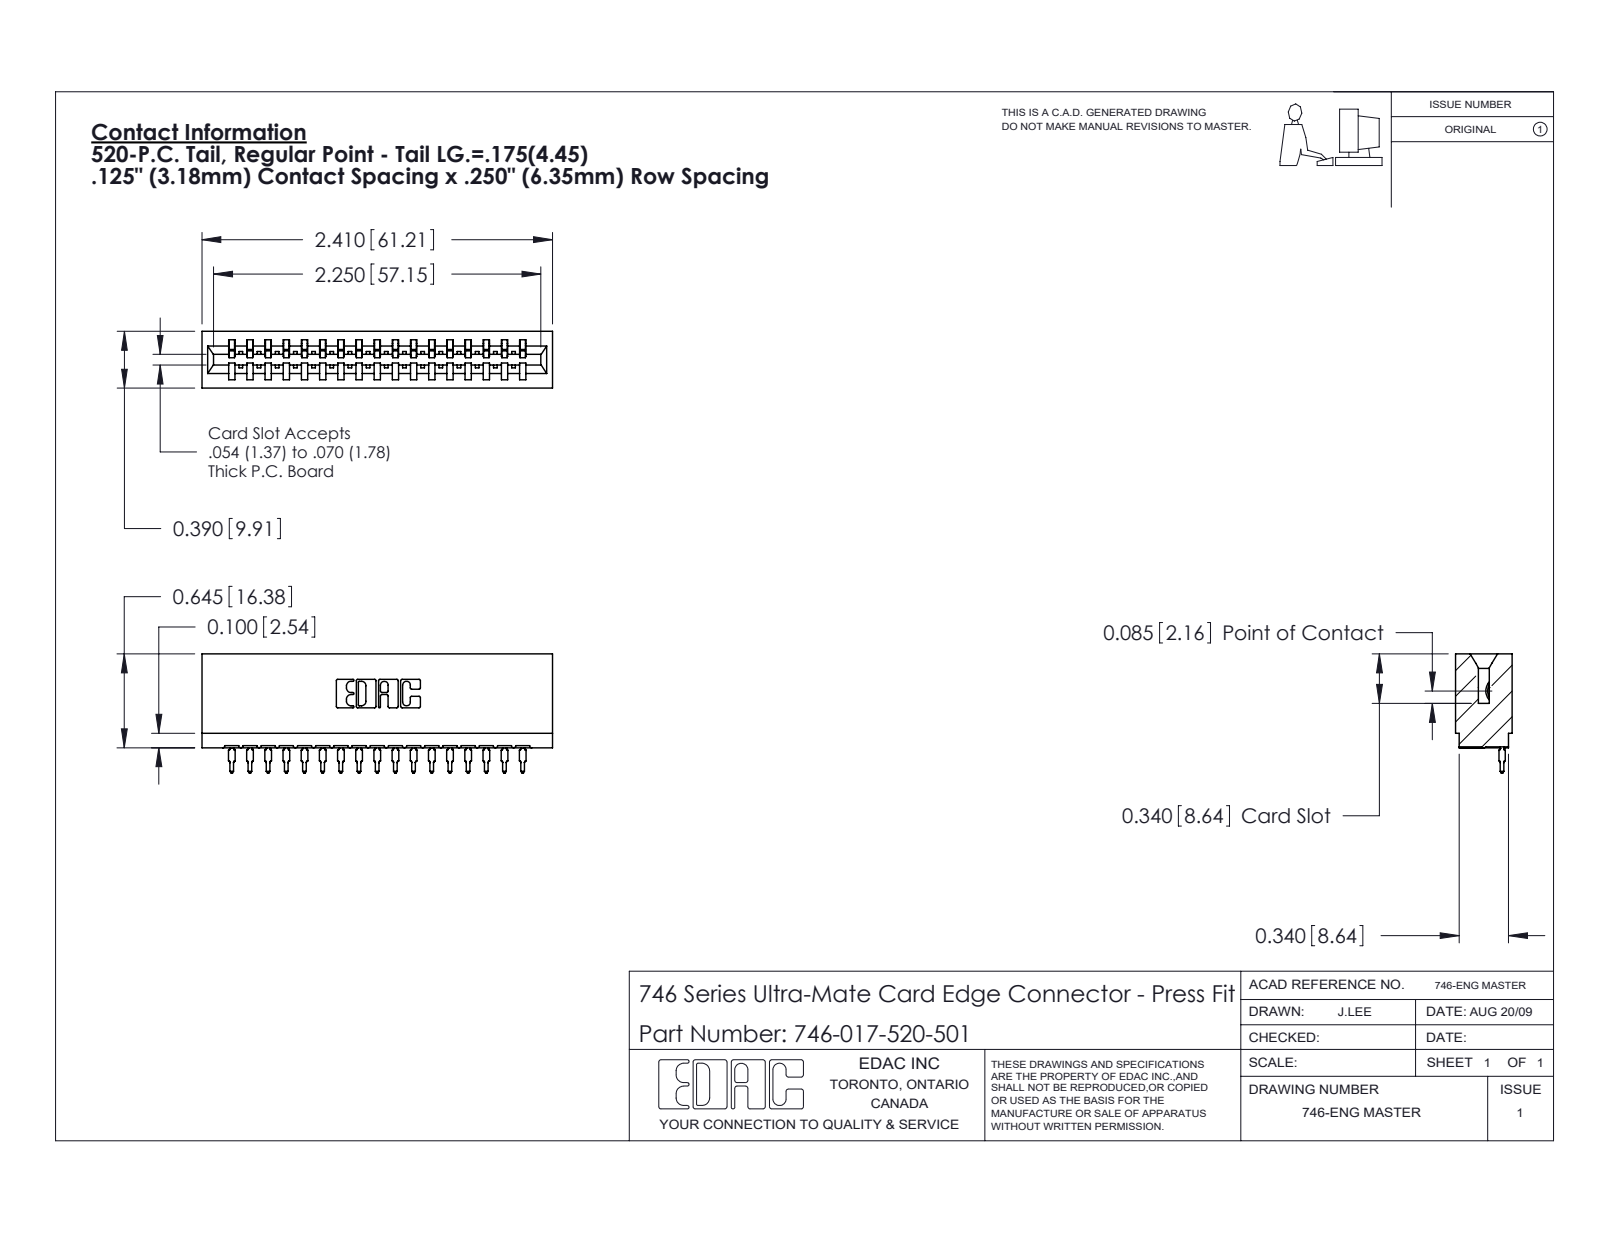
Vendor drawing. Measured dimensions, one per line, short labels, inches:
name: 746-292-001_520; 746-017-520-501; 746 Part_.340 Slot Depth - 01
written by: SolidWorks 2020 (CONFIG_CONTROL_DESIGN)
unit: in
bodies: 18 solids, 1933 faces (1126 planar, 365 cylindrical, 442 other)
size: 2.41 × 0.819 × 0.39
volume: 0.427 in³; area: 13.84 in²
rounds: 34× R0.021, 22× R0.01, 18× R0.015, 6× R0.007, 6× R0.031, 4× R0.005, 4× R0.011, 3× R0.026
face distances: 0.25, 0.057, 0.333, 0.39, 0.5, 0.042, 0.292, 0.375, 0.125, 0.75
